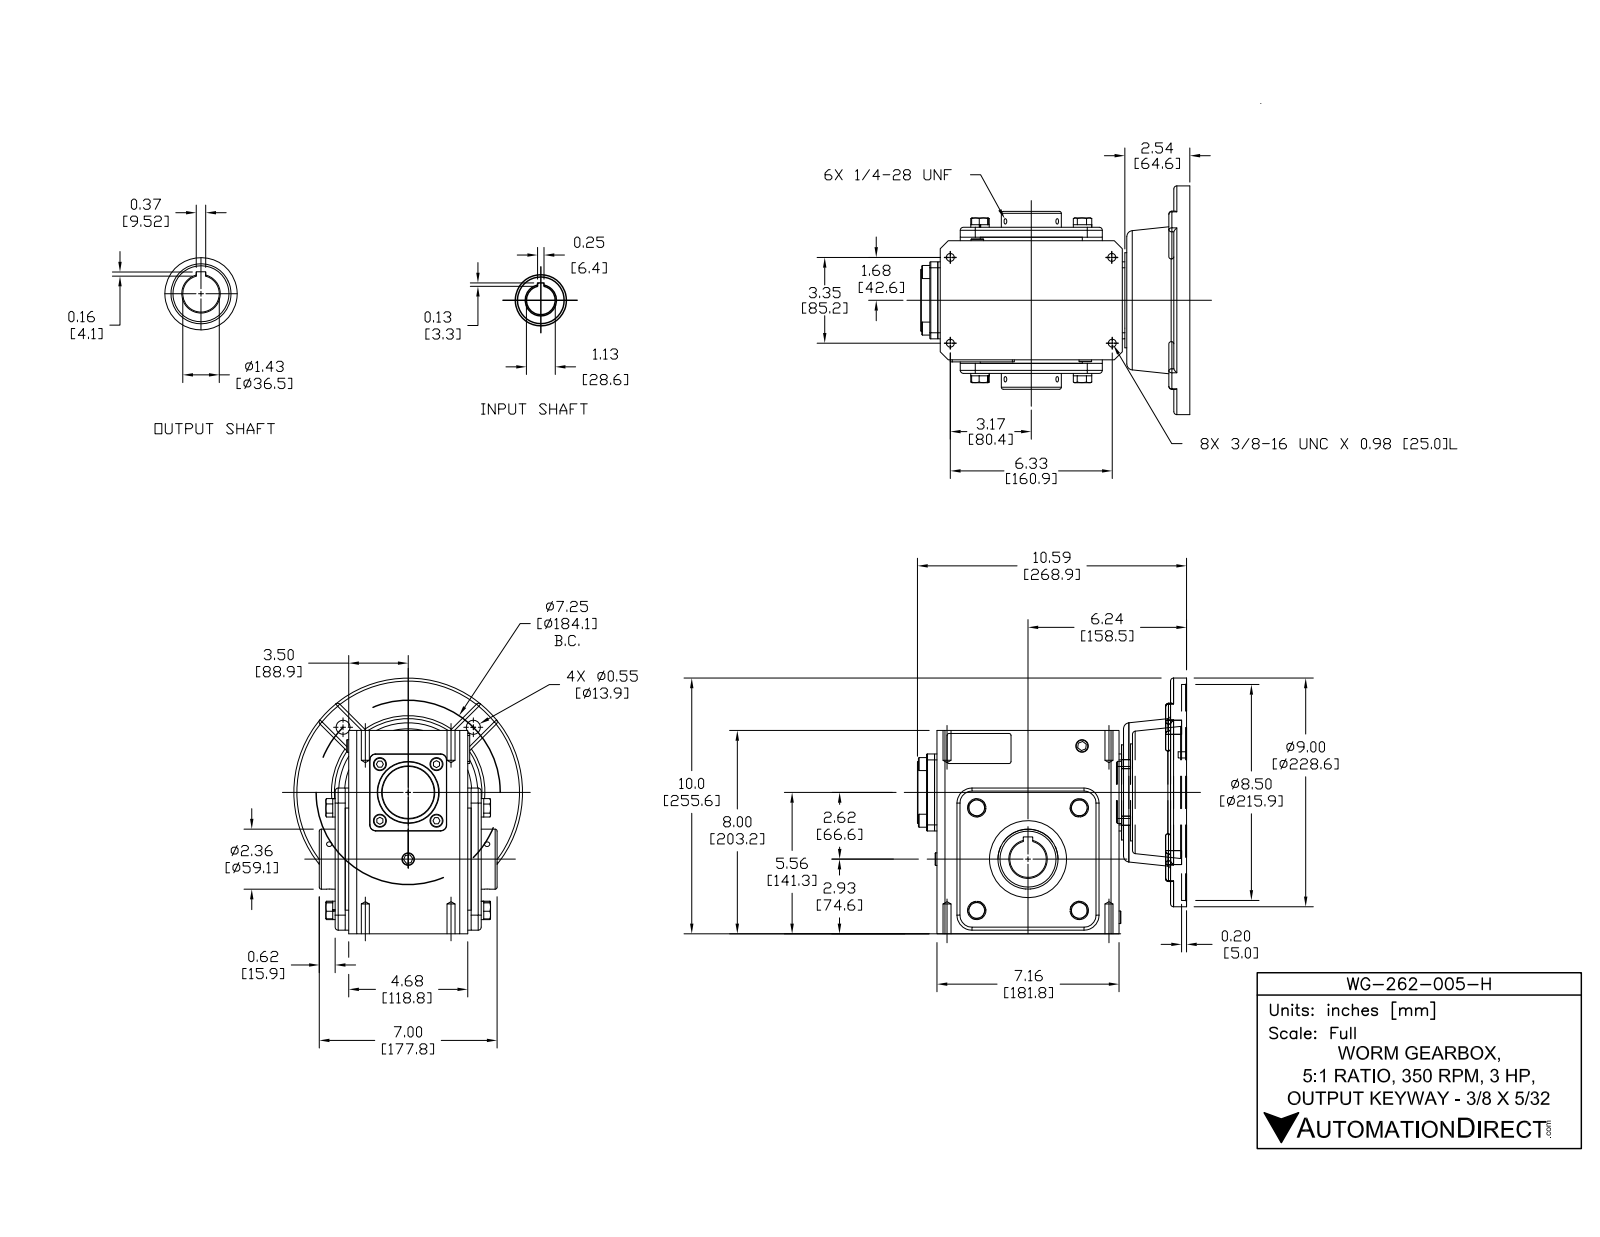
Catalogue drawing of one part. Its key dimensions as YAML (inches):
part_name: "WG-262-005-H"
step_written_by: "SolidWorks 2015 (CONFIG_CONTROL_DESIGN)"
units: inches
bodies: {solids: 32, faces: 553, planar: 277, cylindrical: 160, other: 116}
overall_size: [10.591, 10.063, 9]
volume: 313.4
surface_area: 819.4
round_holes:
  - {diameter: 0.213, count: 6}
  - {diameter: 0.313, count: 4}
  - {diameter: 0.551, count: 4}
  - {diameter: 0.591, count: 1}
  - {diameter: 1.125, count: 1}
  - {diameter: 1.437, count: 1}
  - {diameter: 2.047, count: 1}
  - {diameter: 2.362, count: 1}
  - {diameter: 3.031, count: 1}
  - {diameter: 3.819, count: 1}
  - {diameter: 8.5, count: 1}
round_bosses_or_shafts:
  - {diameter: 0.724, count: 4}
  - {diameter: 0.512, count: 4}
  - {diameter: 9, count: 1}
  - {diameter: 3.74, count: 1}
  - {diameter: 2.441, count: 1}
  - {diameter: 1.772, count: 1}
  - {diameter: 1.142, count: 1}
partial_cylinders:
  - {radius: 0.118, count: 20}
  - {radius: 0.079, count: 6}
  - {radius: 0.236, count: 4}
  - {radius: 0.591, count: 4}
  - {radius: 0.787, count: 4}
  - {radius: 0.02, count: 2}
  - {radius: 0.039, count: 2}
face_to_face_distances: [4.961, 0.394, 0.531, 5.217, 5.354, 0.138, 4.823, 8, 0.433, 2.028]
hole_center_spacings: [3.489, 3.625, 5.127, 5.757, 6.213, 2.564, 3.375, 5.787]
